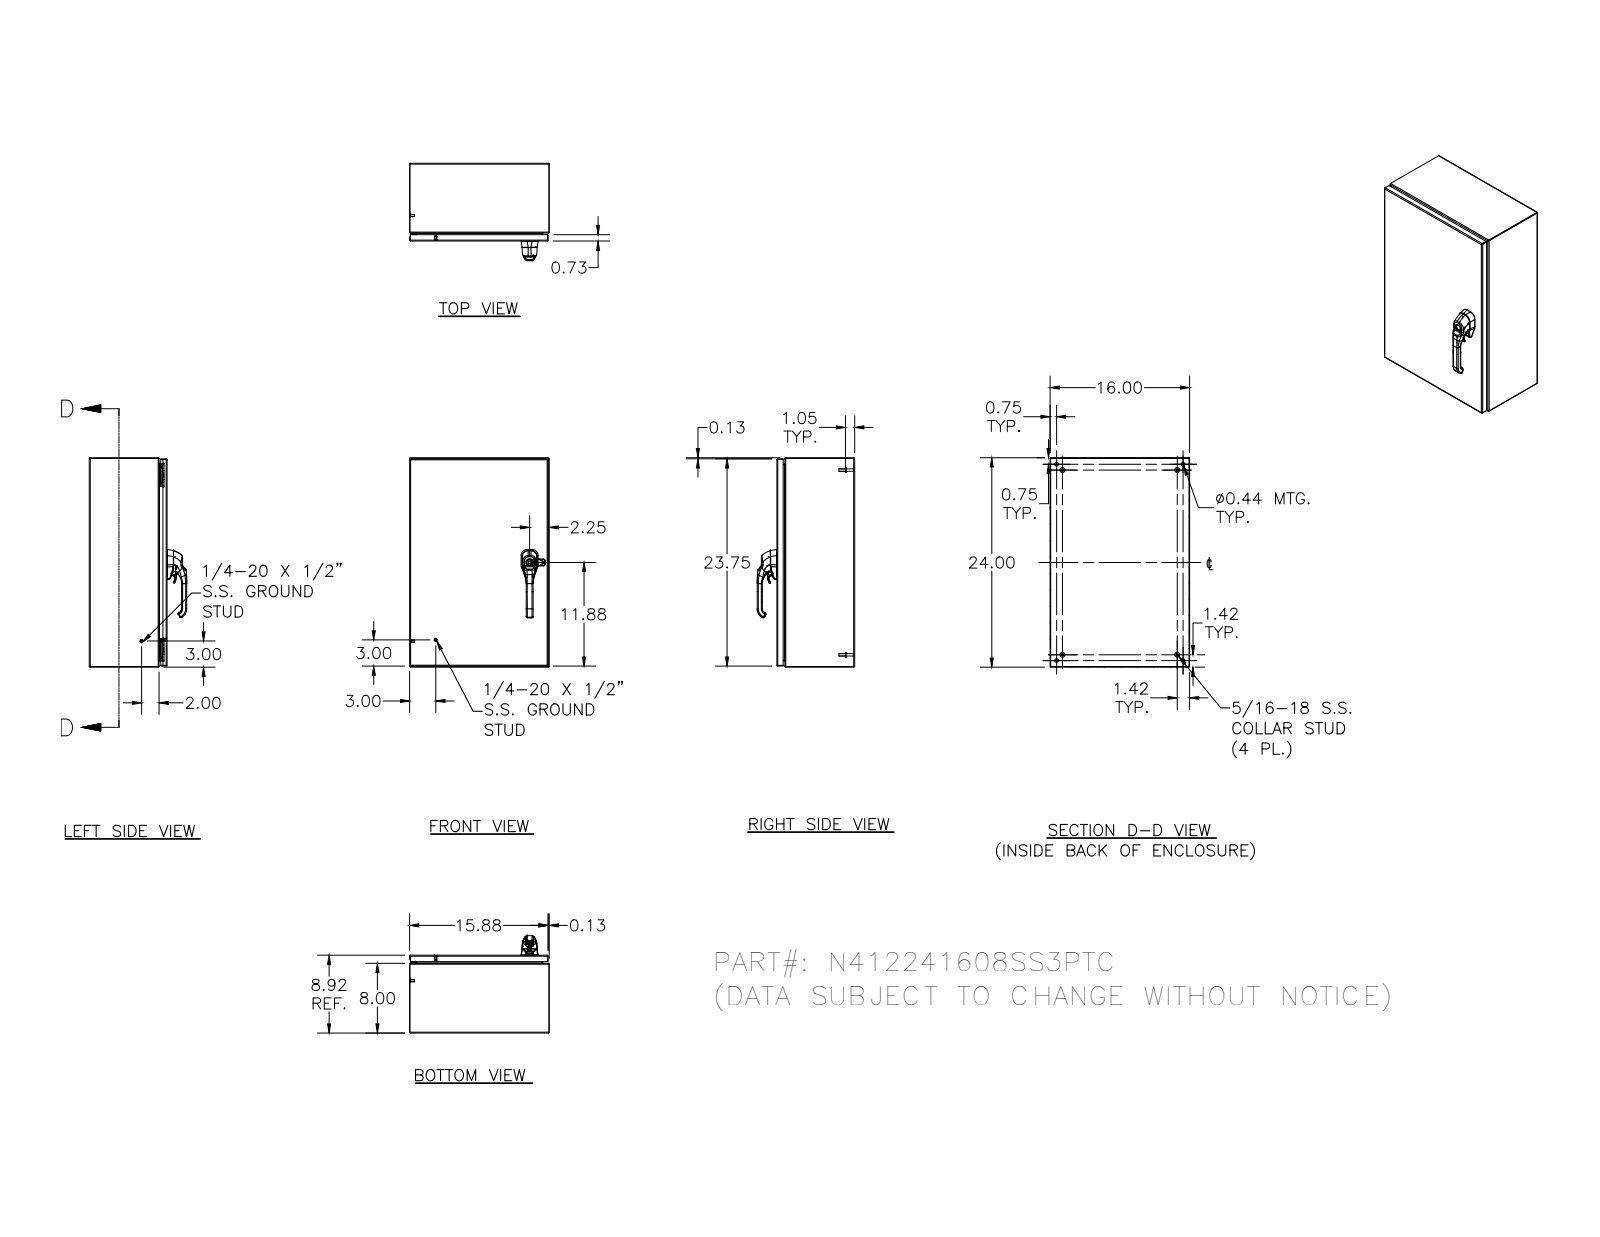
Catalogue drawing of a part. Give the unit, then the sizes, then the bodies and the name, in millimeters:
Units: millimetres
Overall size (bounding box): 609.6 × 406.4 × 283.6
Round holes (diameter × count): ⌀2.4 ×4, ⌀3.9 ×4, ⌀4.2 ×4, ⌀4.4 ×4, ⌀4.8 ×4, ⌀11.1 ×4, ⌀5.4 ×3, ⌀4 ×2, ⌀8 ×2, ⌀10.2 ×2, ⌀10.5 ×2, ⌀3.1 ×1
Round bosses / shafts (diameter × count): ⌀6.4 ×10, ⌀14.3 ×4, ⌀9.1 ×4, ⌀8.1 ×4, ⌀7.6 ×4, ⌀7 ×4, ⌀6.5 ×4, ⌀4.2 ×4
Partial cylindrical surfaces — rounded edges, fillets, slot ends (radius × count): R0.5 ×173, R0.3 ×101, R0.8 ×30, R1.3 ×26, R0.5 ×21, R2.7 ×20, R0.4 ×18, R2 ×14
Main face-to-face distances: 1.9, 224.6, 404.5, 226.5, 222.7, 607.7, 402.6, 406.4, 609.6, 605.8
Hole centre spacings: 507.9, 0.4, 16.8, 524.7, 0.5, 12.7, 16.5, 16.7
Volume: 2 019 000 mm³ · Surface area: 2 096 000 mm²
Bodies: 41 solids, 2767 faces (882 planar, 1020 cylindrical, 865 other)
Part name (STEP PRODUCT): N412241608SS3PTC; N412241608SS3PTCBKP; N4122416SS3PTCLID; HFW328176 (+8 more)
STEP written by: Autodesk Inventor 2011 (AUTOMOTIVE_DESIGN)
